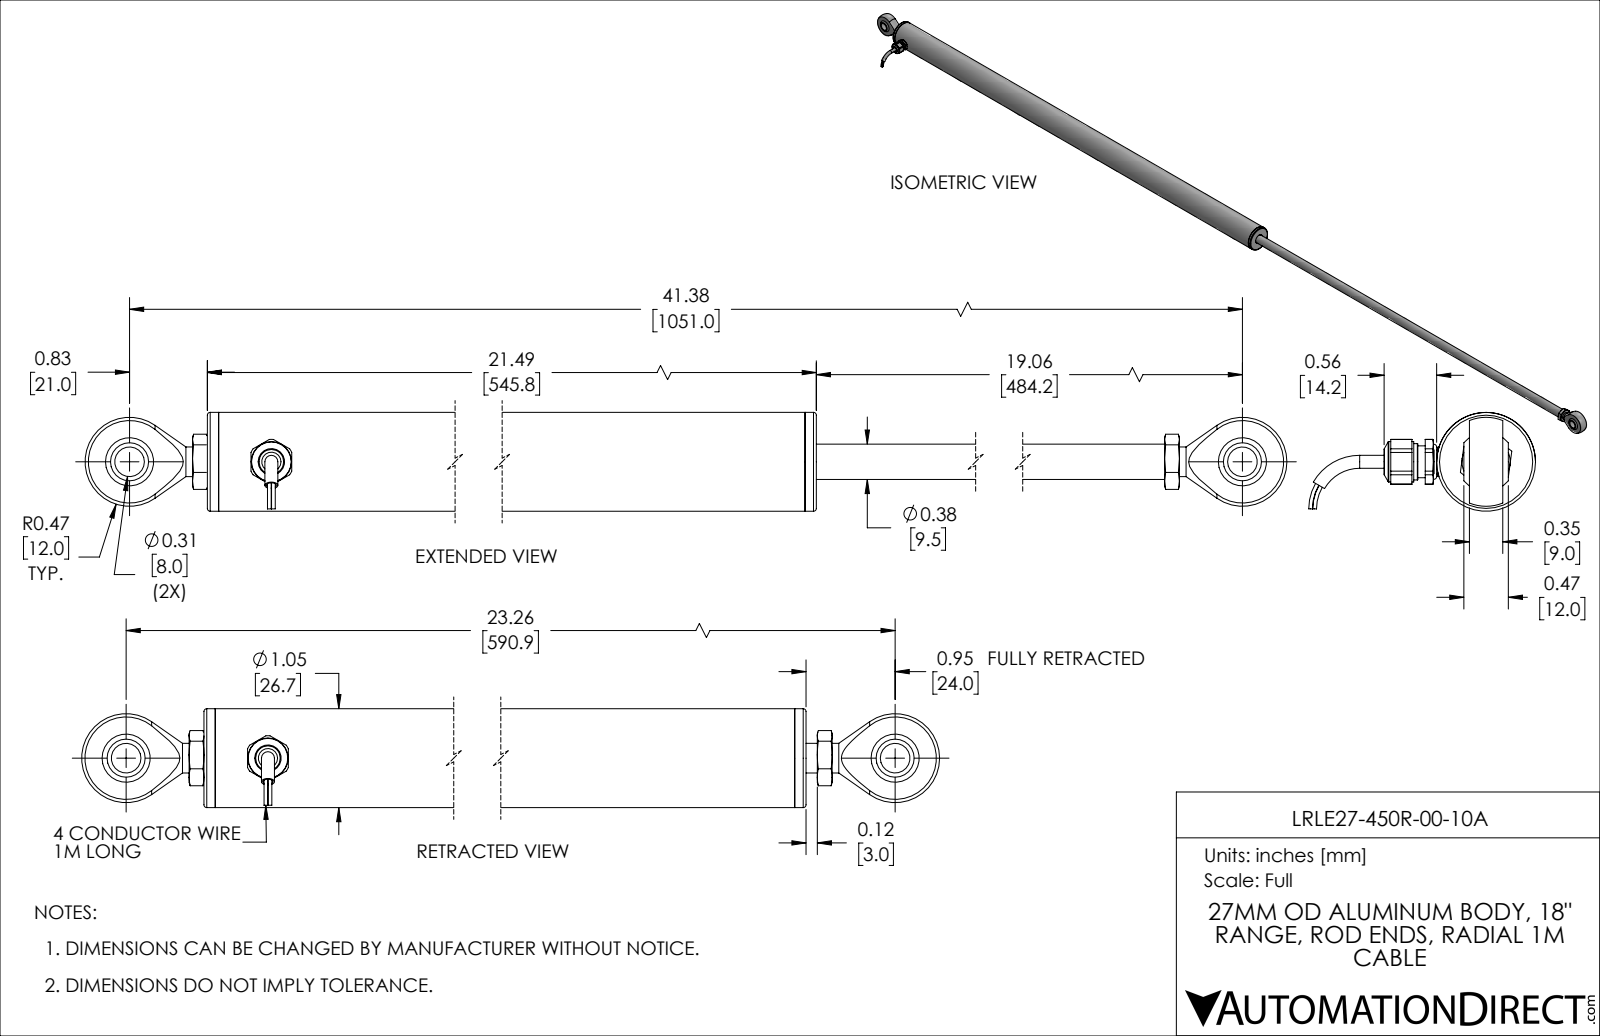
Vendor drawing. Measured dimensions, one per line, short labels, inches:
name: LRLE27-450R-00-10A
written by: SolidWorks 2019 (AUTOMOTIVE_DESIGN)
unit: in
bodies: 28 solids, 300 faces (114 planar, 92 cylindrical, 94 other)
size: 24.088 × 2.409 × 1.05
volume: 10.44 in³; area: 214.2 in²
holes: 2× ⌀0.268, 1× ⌀0.106, 1× ⌀0.138, 1× ⌀0.156, 1× ⌀0.187, 1× ⌀0.201, 1× ⌀0.205, 1× ⌀0.272, 1× ⌀0.275, 1× ⌀0.313, 1× ⌀0.36, 1× ⌀0.375
bosses: 4× ⌀0.315, 4× ⌀0.039, 1× ⌀1.05, 1× ⌀0.85, 1× ⌀0.848, 1× ⌀0.685, 1× ⌀0.625, 1× ⌀0.5
rounds: 2× R0.01, 2× R0.067, 2× R0.25, 1× R0.197, 1× R0.224, 1× R0.238, 1× R0.344, 1× R0.407
face distances: 0.12, 21.37, 0.354, 21.49, 0.737, 20.753, 0.5, 1.65, 0.913, 19.84
